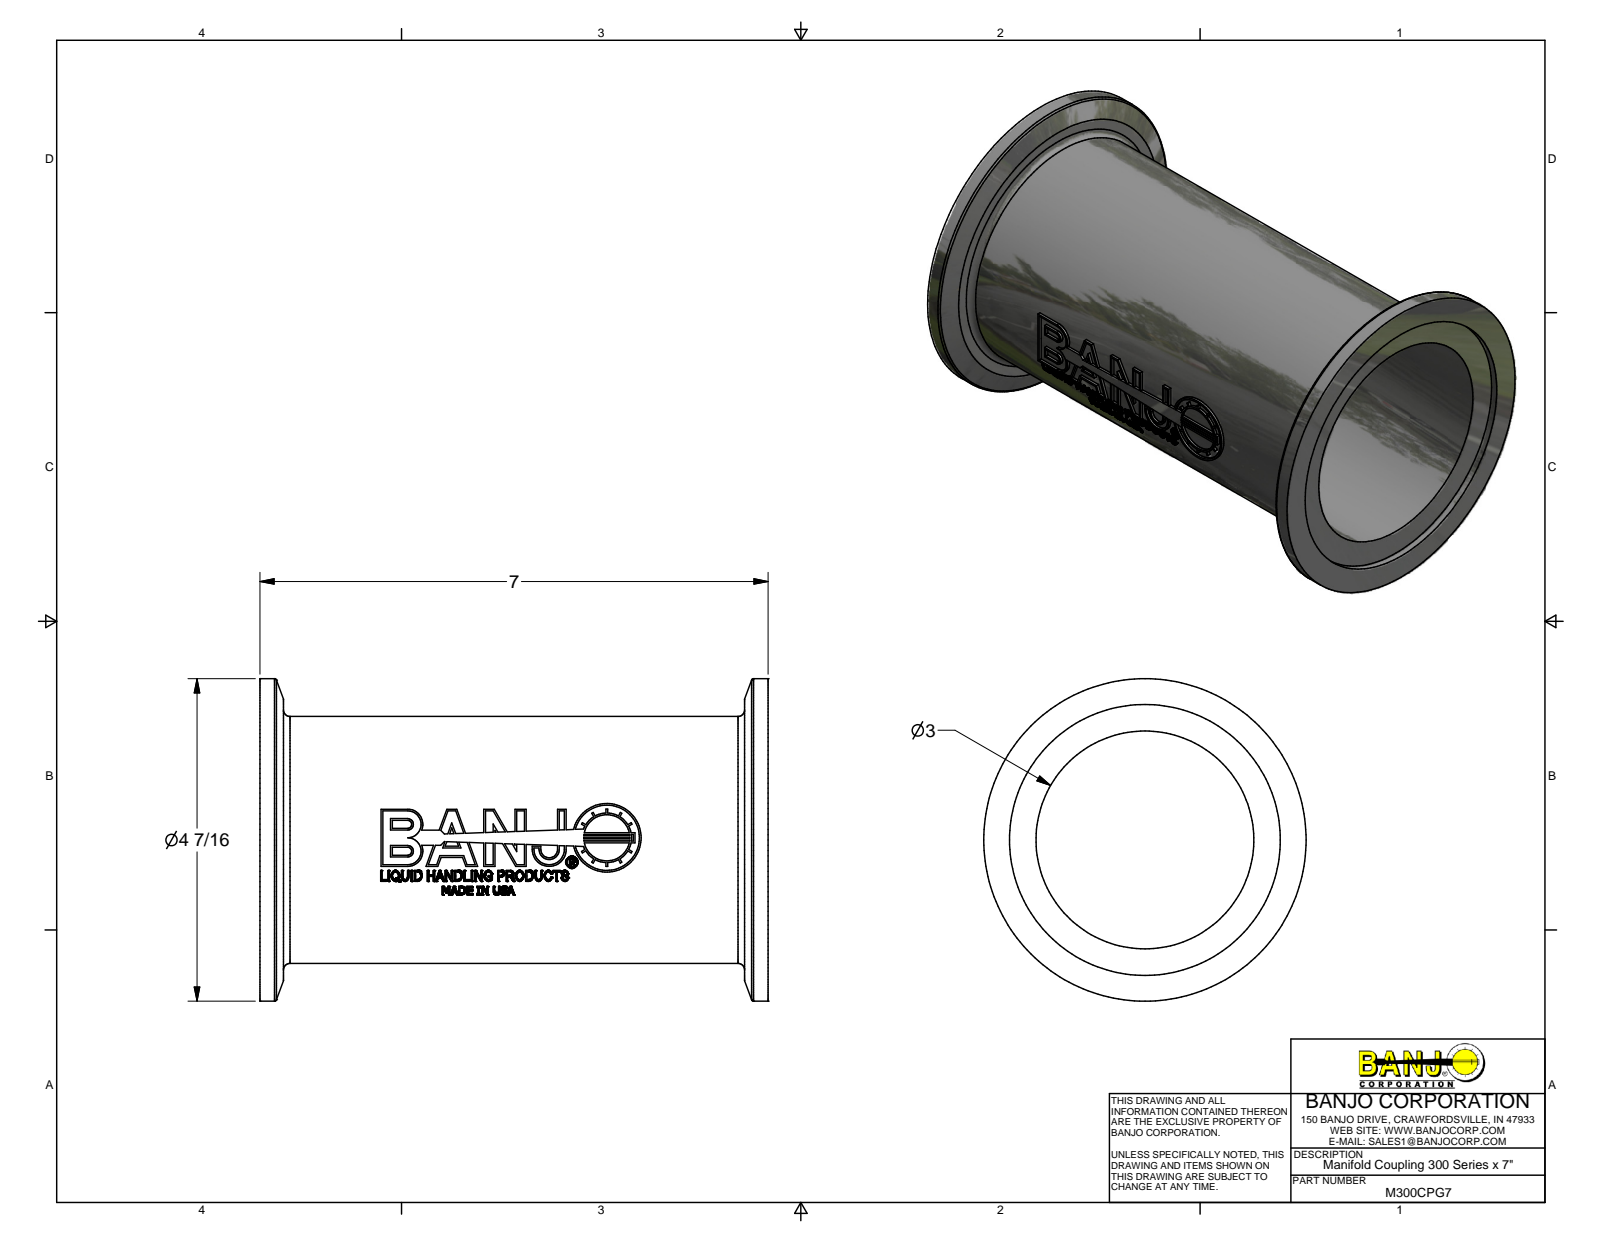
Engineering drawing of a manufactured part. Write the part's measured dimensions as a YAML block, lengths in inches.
part_name: "M300CPG7"
step_written_by: "Autodesk Inventor 2012 (AUTOMOTIVE_DESIGN)"
units: inches
bodies: {solids: 43, faces: 830, planar: 412, cylindrical: 144, other: 274}
overall_size: [7, 4.44, 4.429]
volume: 17.64
surface_area: 172.1
round_holes:
  - {diameter: 0.635, count: 1}
  - {diameter: 0.898, count: 1}
  - {diameter: 3, count: 1}
  - {diameter: 3.4, count: 1}
  - {diameter: 3.73, count: 1}
round_bosses_or_shafts:
  - {diameter: 4.44, count: 1}
  - {diameter: 0.945, count: 1}
partial_cylinders:
  - {radius: 0.055, count: 2}
  - {radius: 0.079, count: 2}
  - {radius: 0.156, count: 2}
  - {radius: 0.185, count: 2}
  - {radius: 0.209, count: 2}
  - {radius: 0.115, count: 1}
  - {radius: 0.139, count: 1}
  - {radius: 0.21, count: 1}
face_to_face_distances: [0.1, 6.9, 7, 6.8, 0.04, 0.024, 1.544, 1.584, 0.313, 1.856]
